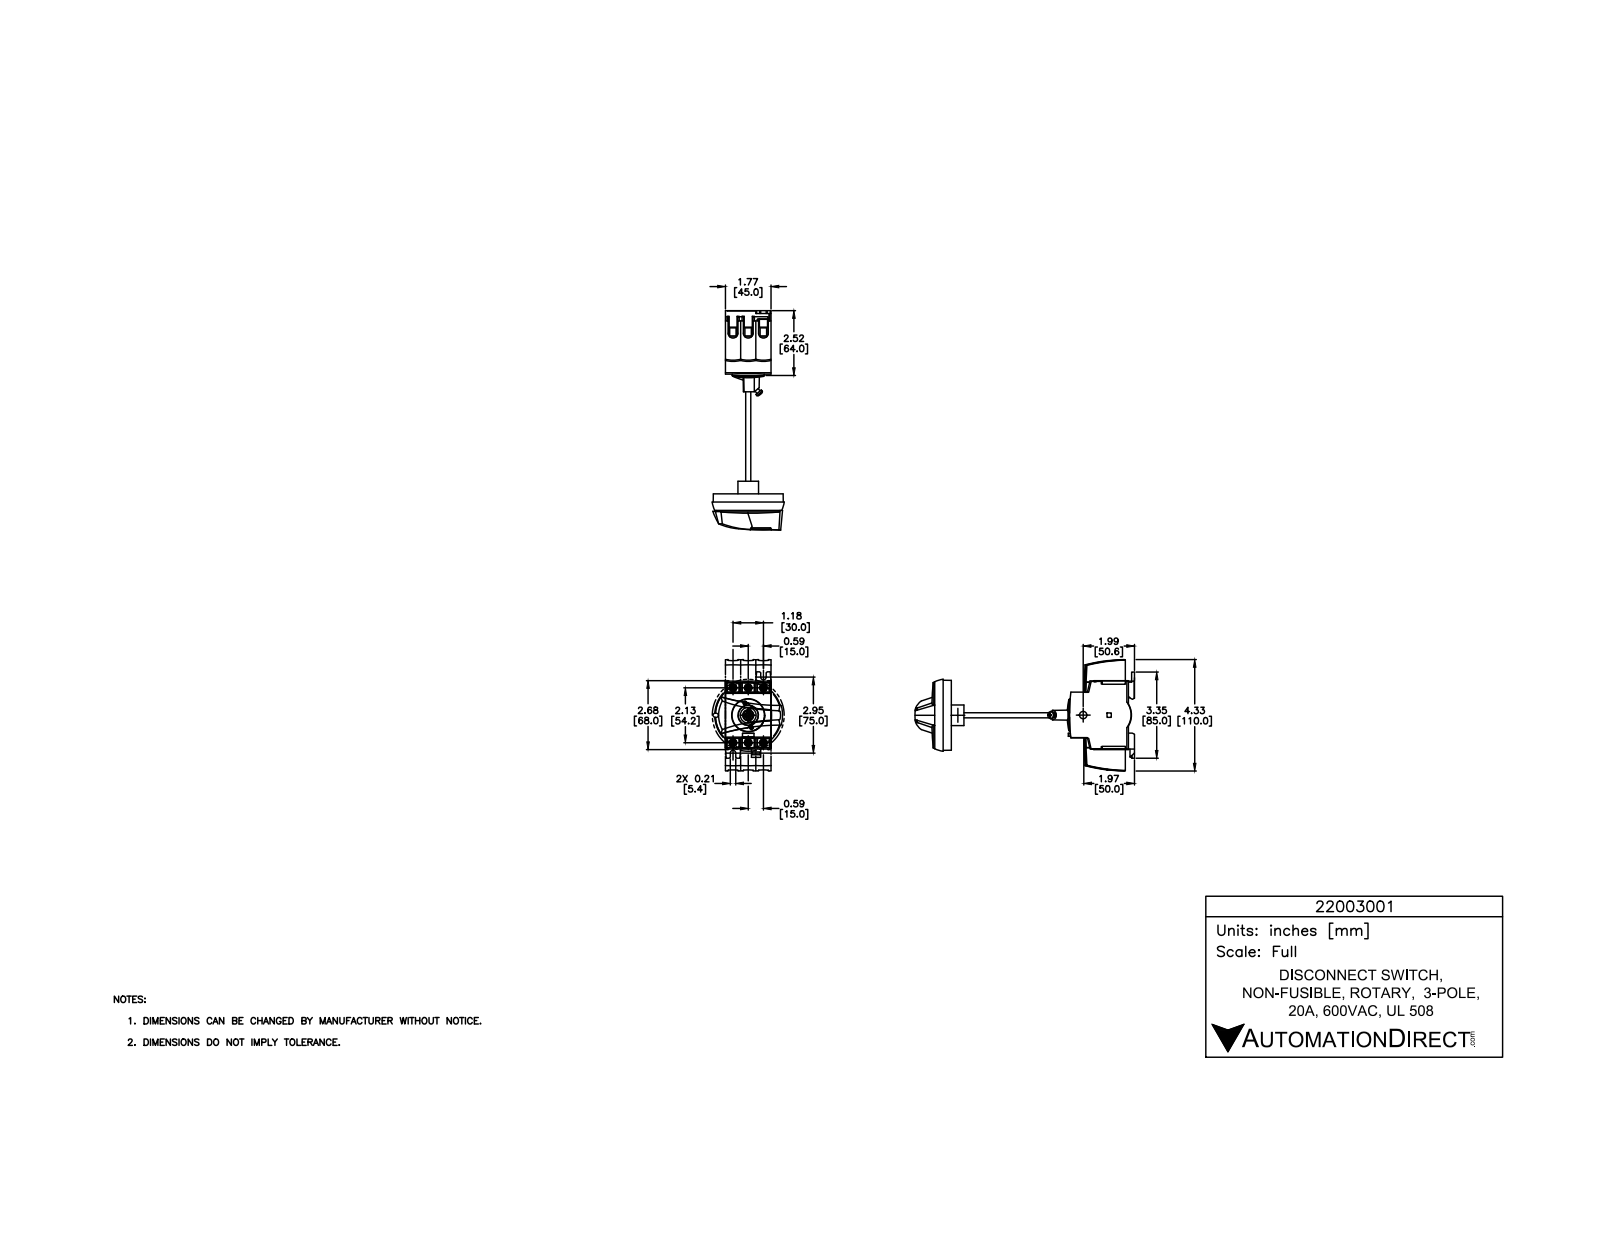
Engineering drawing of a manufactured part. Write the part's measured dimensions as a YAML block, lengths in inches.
part_name: "22003001-UL"
step_written_by: "SolidWorks 2021 (CONFIG_CONTROL_DESIGN)"
units: inches
bodies: {solids: 1, faces: 463, planar: 389, cylindrical: 50, other: 24}
overall_size: [3.346, 2.571, 1.772]
volume: 9.498
surface_area: 40.23
round_holes:
  - {diameter: 0.26, count: 6}
  - {diameter: 0.283, count: 1}
  - {diameter: 1.244, count: 1}
partial_cylinders:
  - {radius: 0.012, count: 13}
  - {radius: 0.02, count: 5}
  - {radius: 0.165, count: 4}
  - {radius: 0.039, count: 3}
  - {radius: 0.106, count: 2}
  - {radius: 0.13, count: 1}
  - {radius: 0.354, count: 1}
  - {radius: 0.37, count: 1}
face_to_face_distances: [1.772, 0.433, 2.205, 2.157, 2.638, 2.28, 0.591, 2.591, 0.047, 0.386]
hole_center_spacings: [0.591, 1.219, 2.214, 2.134, 1.067, 1.181, 2.439]
